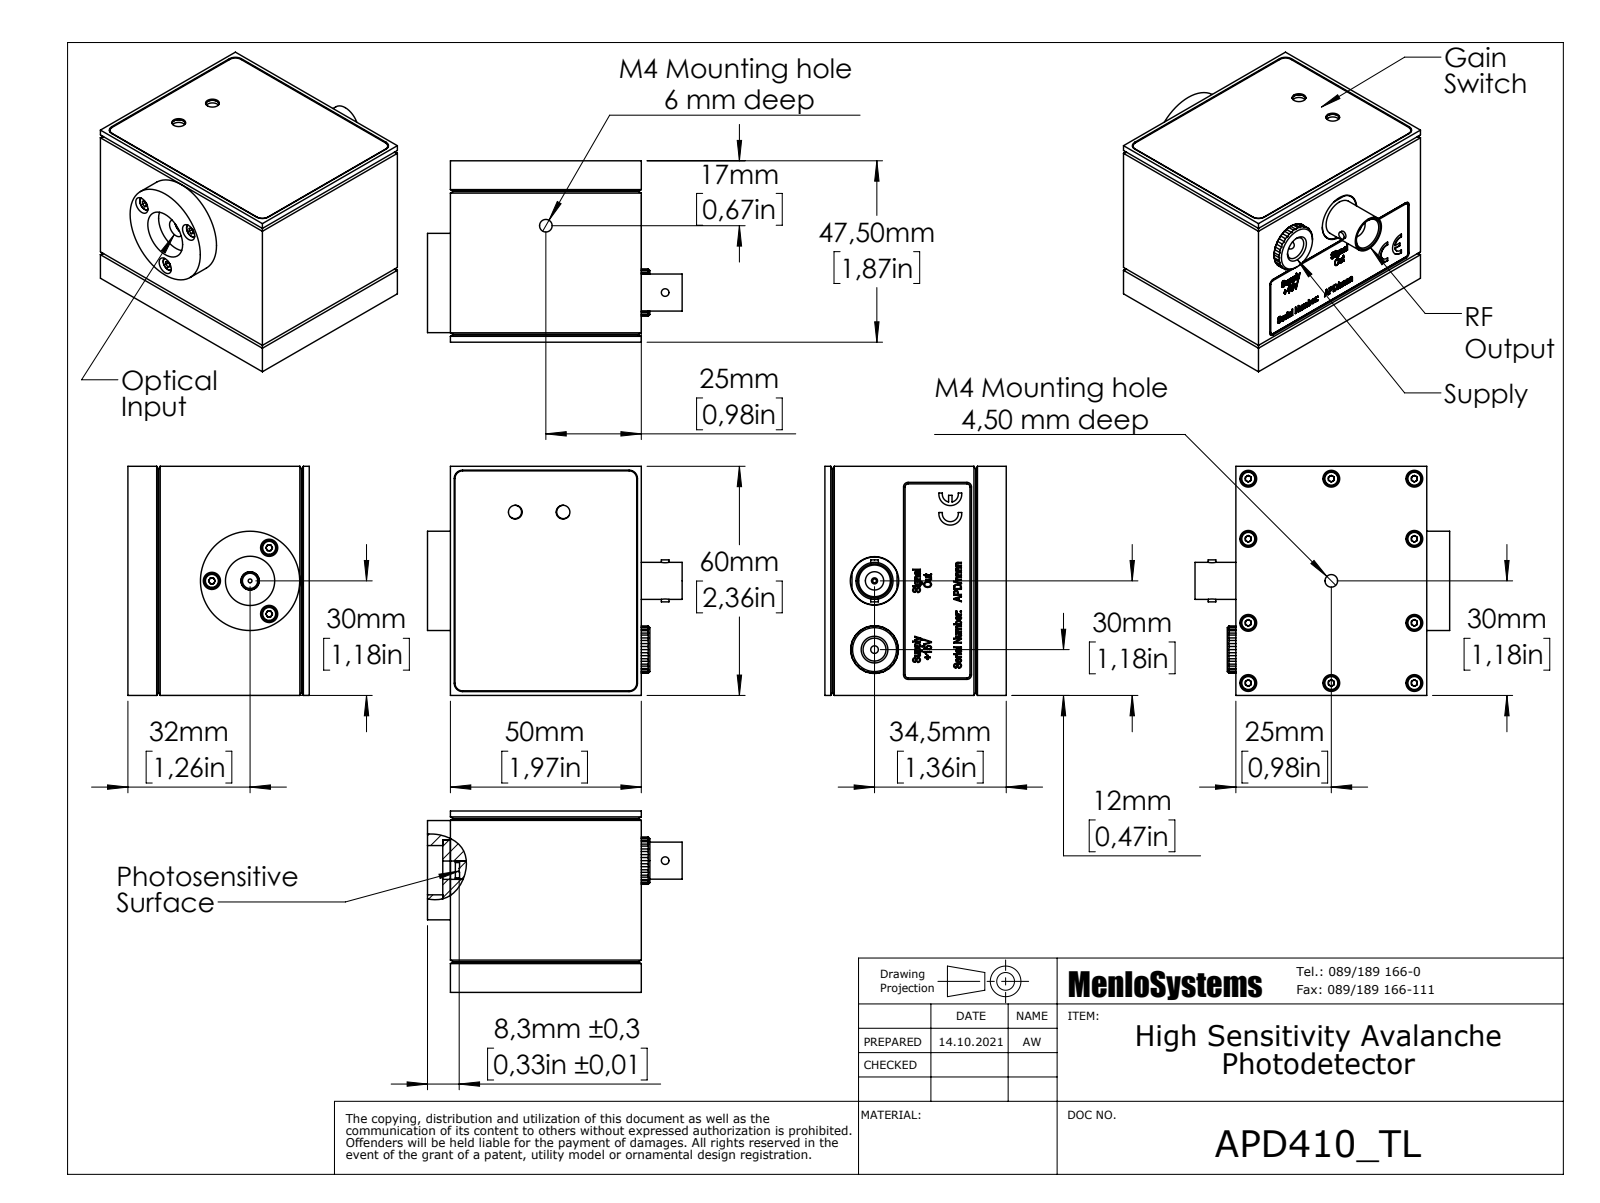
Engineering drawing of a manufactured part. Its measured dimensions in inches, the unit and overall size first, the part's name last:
Units: inches
Overall size (bounding box): 2.626 × 2.362 × 1.87
Round holes (diameter × count): ⌀0.063 ×27, ⌀0.157 ×11, ⌀0.087 ×10, ⌀0.094 ×10, ⌀0.173 ×10, ⌀0.083 ×3, ⌀0.177 ×3, ⌀0.13 ×2, ⌀0.142 ×2, ⌀0.165 ×2, ⌀0.197 ×2, ⌀0.344 ×2
Round bosses / shafts (diameter × count): ⌀0.079 ×15, ⌀0.15 ×13, ⌀0.02 ×3, ⌀0.425 ×2, ⌀0.343 ×2, ⌀0.323 ×2, ⌀0.29 ×2, ⌀1.024 ×1
Partial cylindrical surfaces — rounded edges, fillets, slot ends (radius × count): R0.118 ×10, R0.098 ×6, R0.031 ×4, R0.047 ×4, R0.079 ×4, R0.087 ×4, R0.033 ×2, R0.083 ×2
Main face-to-face distances: 1.772, 0.197, 0.014, 0.059, 0.453, 0.02, 1.852, 1.866, 1.791, 0.315
Hole centre spacings: 0.61, 0.62, 0.846, 0.856, 0.866, 1.476, 1.486, 1.703
Volume: 4.744 in³ · Surface area: 79.58 in²
Bodies: 25 solids, 1539 faces (724 planar, 363 cylindrical, 452 other)
Part name (STEP PRODUCT): APD310_2020805
STEP written by: SolidWorks 2018 (AUTOMOTIVE_DESIGN)
